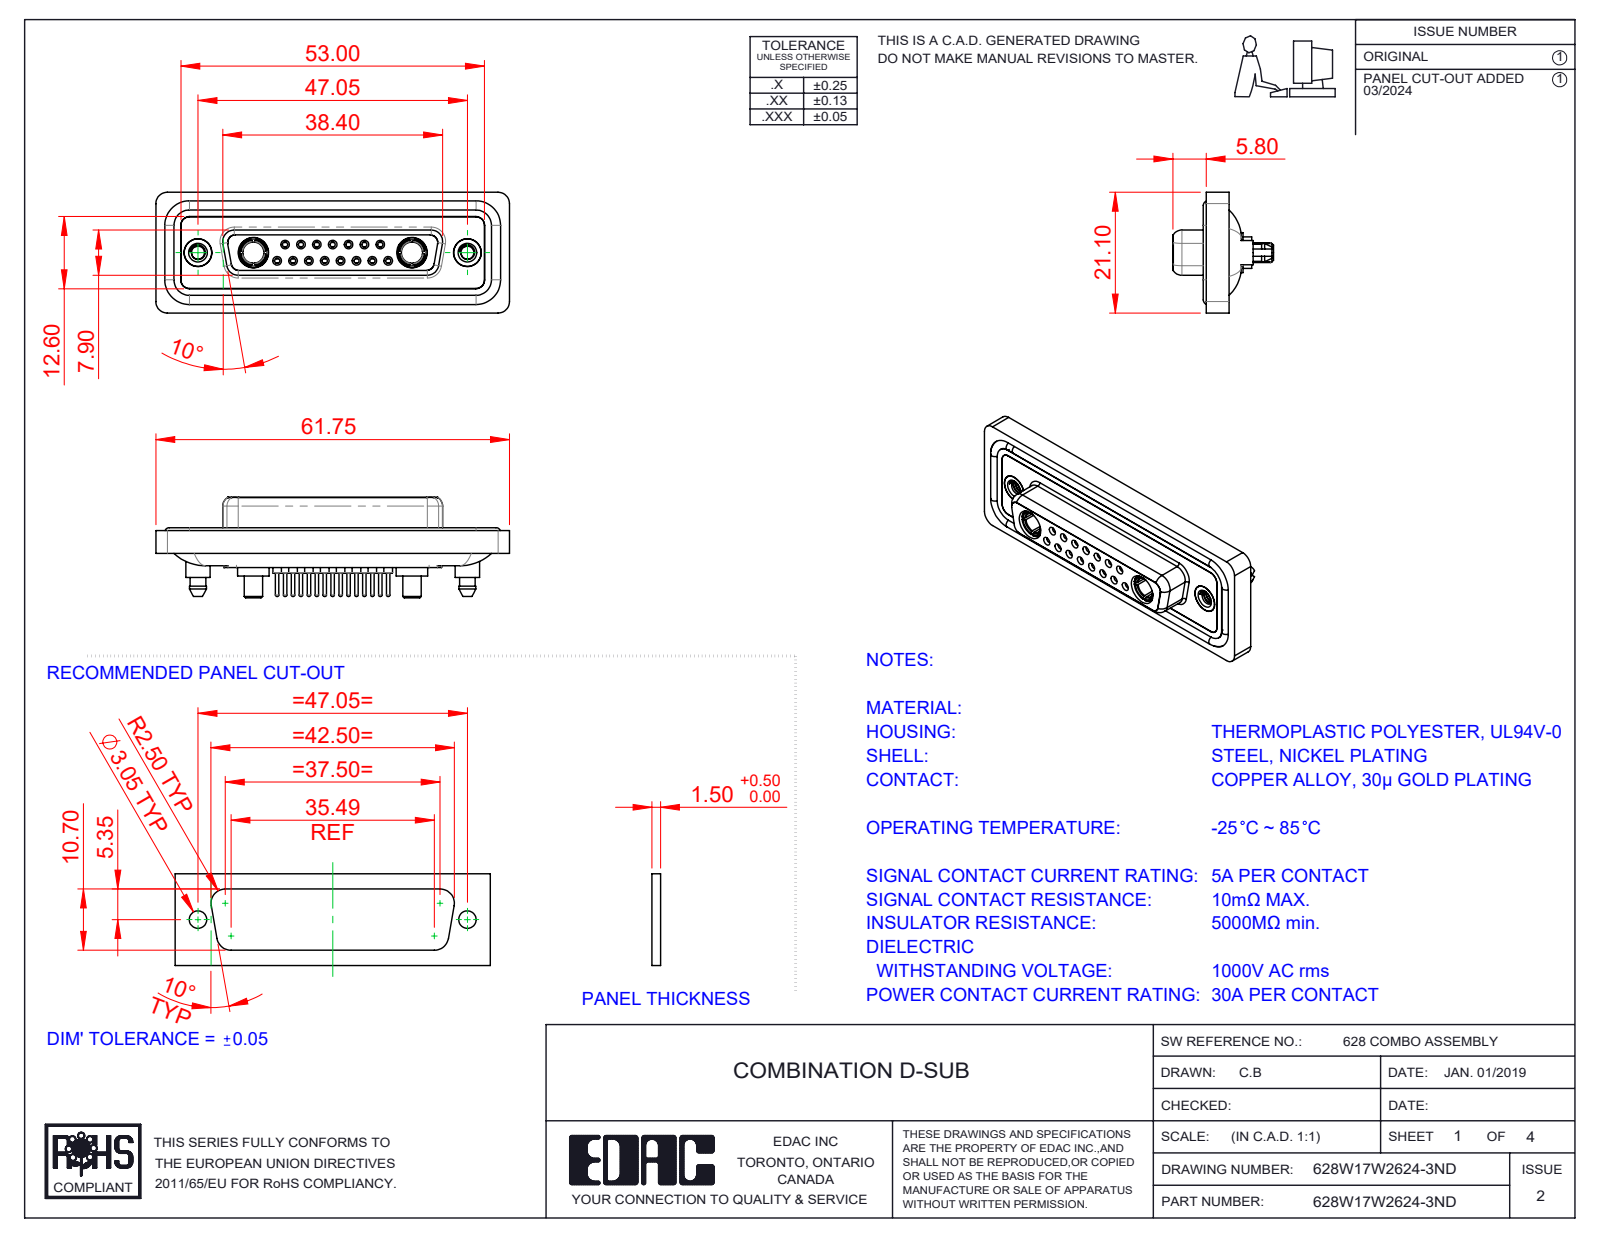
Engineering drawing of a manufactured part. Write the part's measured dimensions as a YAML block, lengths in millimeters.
part_name: "628W17W2624-3ND; 628Combo Contact Row 2_24; 628Combo Waterproof Housing_25 Contacts; Power Socket_30A S (+5 more)"
step_written_by: "SolidWorks 2023 (CONFIG_CONTROL_DESIGN)"
units: millimeters
bodies: {solids: 26, faces: 1425, planar: 404, cylindrical: 567, other: 454}
overall_size: [61.75, 21.1, 17.55]
volume: 8474
surface_area: 14204
round_holes:
  - {diameter: 0.9, count: 15}
  - {diameter: 1.1, count: 15}
  - {diameter: 1.5, count: 15}
  - {diameter: 2, count: 15}
  - {diameter: 1.6, count: 8}
  - {diameter: 1.7, count: 7}
  - {diameter: 4.85, count: 4}
  - {diameter: 2.26, count: 2}
  - {diameter: 3.7, count: 2}
  - {diameter: 4, count: 2}
  - {diameter: 4.05, count: 2}
  - {diameter: 5, count: 2}
round_bosses_or_shafts:
  - {diameter: 2.2, count: 15}
  - {diameter: 0.6, count: 15}
  - {diameter: 1.6, count: 11}
  - {diameter: 5.5, count: 2}
  - {diameter: 5.4, count: 2}
  - {diameter: 5.2, count: 2}
  - {diameter: 4.96, count: 2}
  - {diameter: 4.95, count: 2}
partial_cylinders:
  - {radius: 1.5, count: 24}
  - {radius: 2, count: 18}
  - {radius: 1.6, count: 10}
  - {radius: 1.35, count: 8}
  - {radius: 0.25, count: 4}
  - {radius: 0.5, count: 4}
  - {radius: 0.6, count: 4}
  - {radius: 0.65, count: 4}
face_to_face_distances: [0.4, 1.8, 7.45, 5.65, 6.6, 0.5, 7.05, 1.6, 2.9, 1.1]
hole_center_spacings: [3.16, 2.77, 8.31, 5.54, 5.03, 5.04, 7.49, 11.08]
